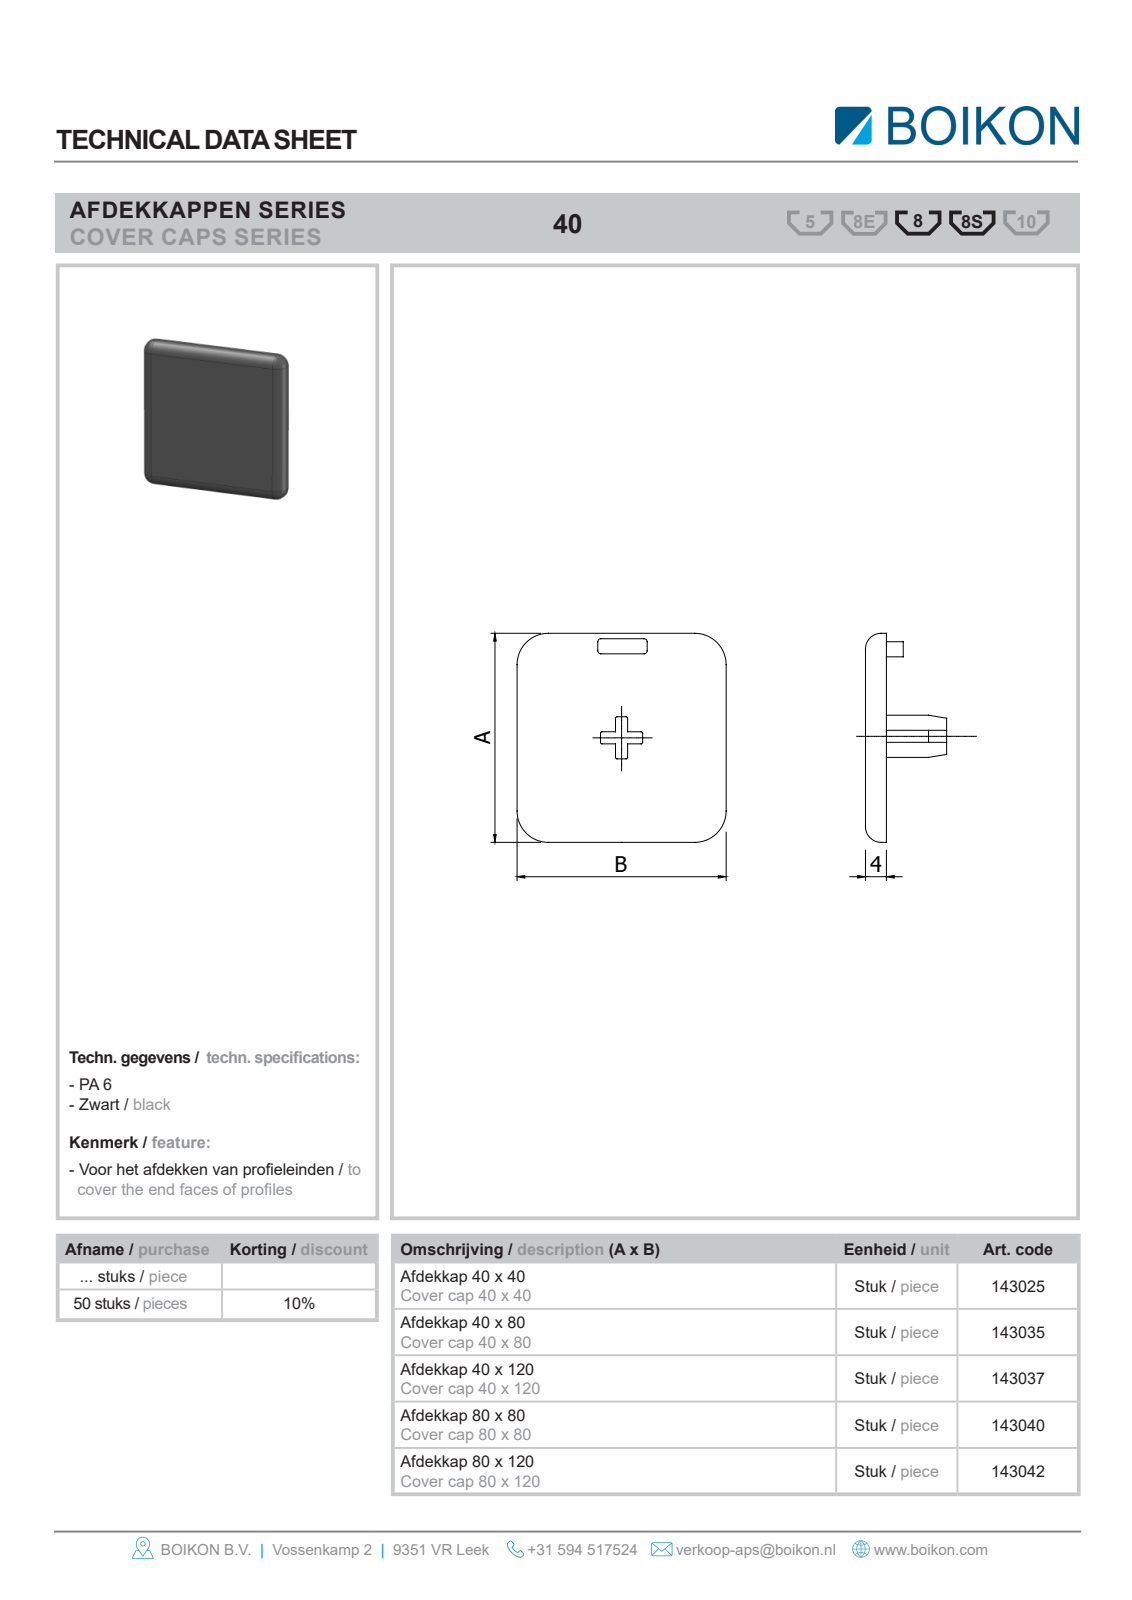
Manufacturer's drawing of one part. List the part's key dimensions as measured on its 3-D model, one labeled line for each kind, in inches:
Part name (STEP PRODUCT): Root; 143040 Afdekkap 80 x 80BOIKON
STEP written by: HiCAD 2013 1802.4 Build 509 (AUTOMOTIVE_DESIGN)
Units: inches
Bodies: 1 solid, 18 faces (6 planar, 8 cylindrical, 4 other)
Overall size (bounding box): 3.15 × 3.15 × 0.157
Volume: 1.524 in³ · Surface area: 21.13 in²
Partial cylindrical surfaces — rounded edges, fillets, slot ends (radius × count): R0.118 ×8
Main face-to-face distances: 0.157, 3.15
